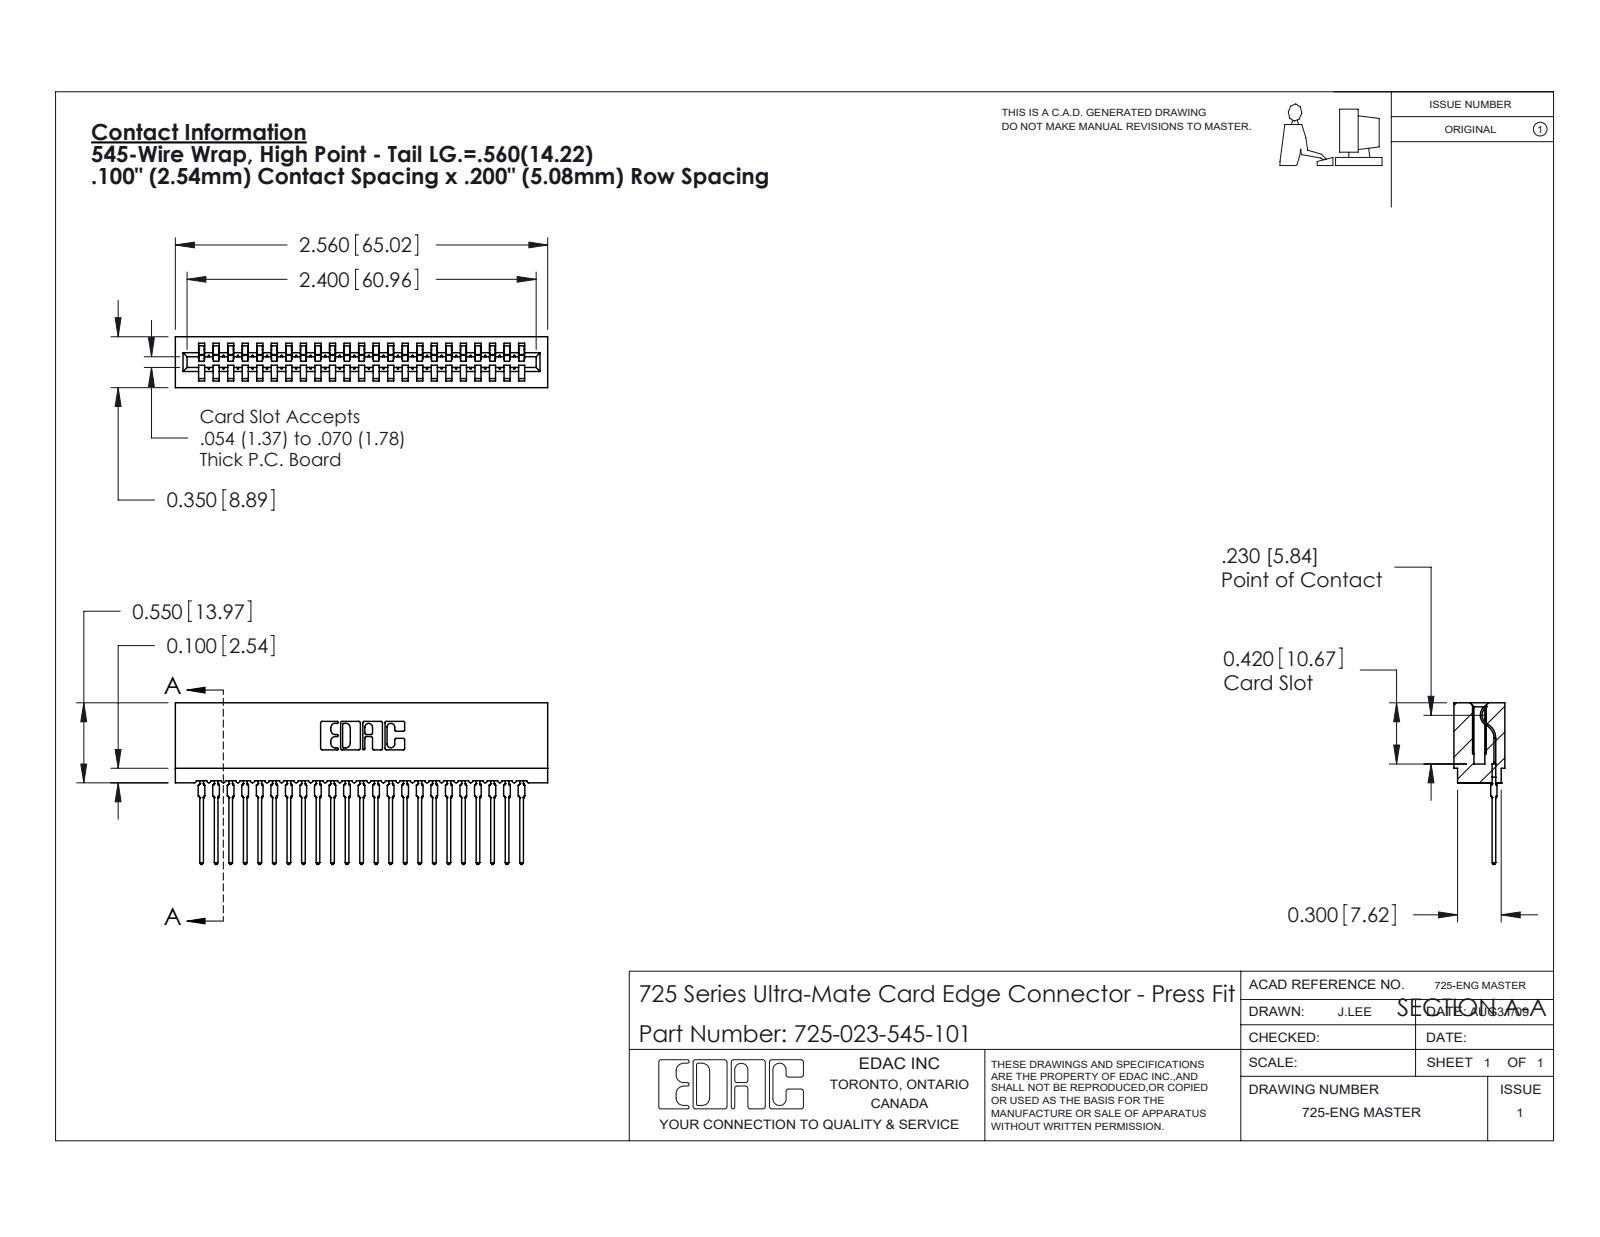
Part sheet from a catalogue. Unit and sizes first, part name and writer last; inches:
Units: inches
Overall size (bounding box): 2.56 × 1.111 × 0.35
Partial cylindrical surfaces — rounded edges, fillets, slot ends (radius × count): R0.015 ×46, R0.021 ×46, R0.01 ×22, R0.007 ×6, R0.031 ×6, R0.005 ×4, R0.011 ×4, R0.026 ×3
Main face-to-face distances: 0.2, 0.1, 0.3, 0.4, 0.5, 0.6, 0.35, 0.7, 0.063, 0.287
Volume: 0.312 in³ · Surface area: 15.23 in²
Bodies: 24 solids, 2671 faces (1596 planar, 477 cylindrical, 598 other)
Part name (STEP PRODUCT): 725-023-545-101; 725 Part_Insulator Option - 01; 745-292-001_545
STEP written by: SolidWorks 2020 (CONFIG_CONTROL_DESIGN)
